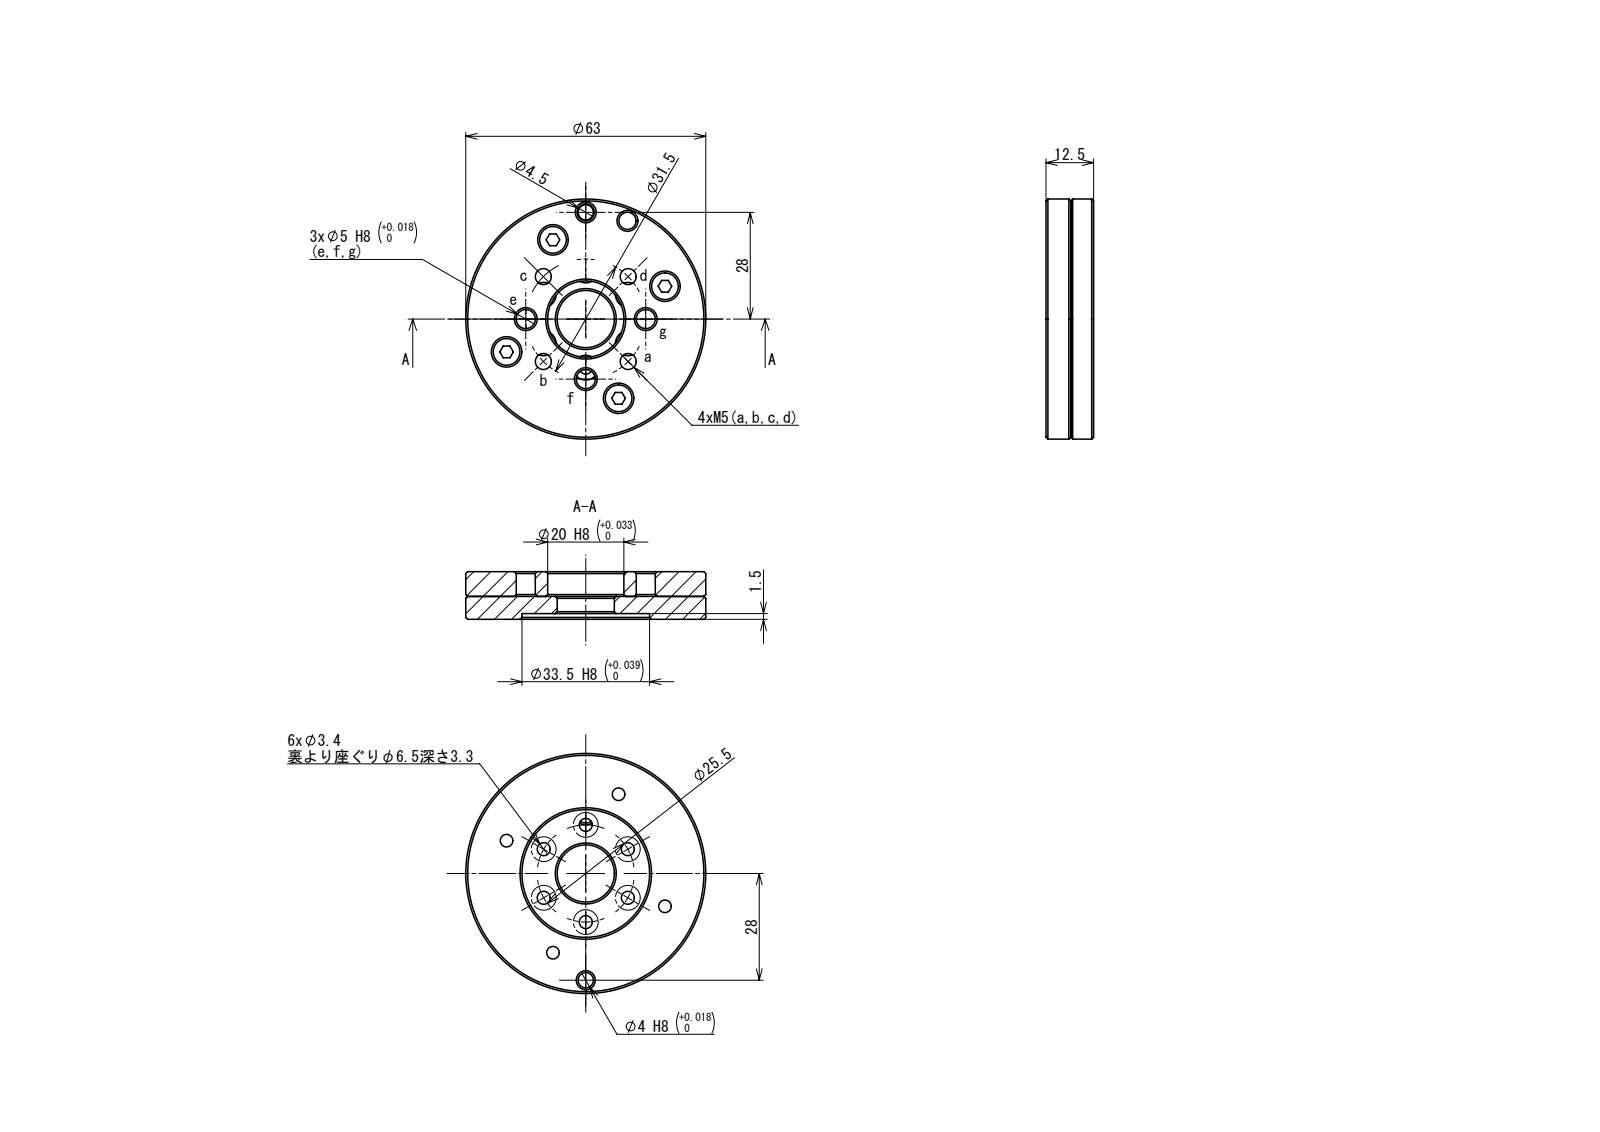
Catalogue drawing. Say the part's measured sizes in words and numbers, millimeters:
The part is named "PDG60-5-1". Its 3-D file was written by "SolidWorks 2020 (CONFIG_CONTROL_DESIGN)". It is 8 solids with 233 faces: 67 planar, 107 cylindrical and 59 other. Overall it measures 63 by 63 by 12.5 millimeters. Its volume is 32 409 cubic millimeters and its surface area 17 175 square millimeters. Round holes: 6 of diameter 3.4, 6 of diameter 4.5, 6 of diameter 6.5, 4 of diameter 3.3, 4 of diameter 4.2, 4 of diameter 8, 3 of diameter 5, 2 of diameter 3, 1 of diameter 4, 1 of diameter 15, 1 of diameter 20, 1 of diameter 33.5. Round bosses or shafts: 4 of diameter 7, 1 of diameter 63. Partial cylindrical surfaces (rounded edges, fillets, slot ends): 2 of radius 1.5. The main face-to-face distances are 6.5, 6, 12.5, 1.5, 4.5, 11, 2.1, 8.1, 6.6, 4.4. The hole center spacings are 12.75, 9.98, 37.54, 21.98, 32.03, 15.75, 12.06, 22.5.
